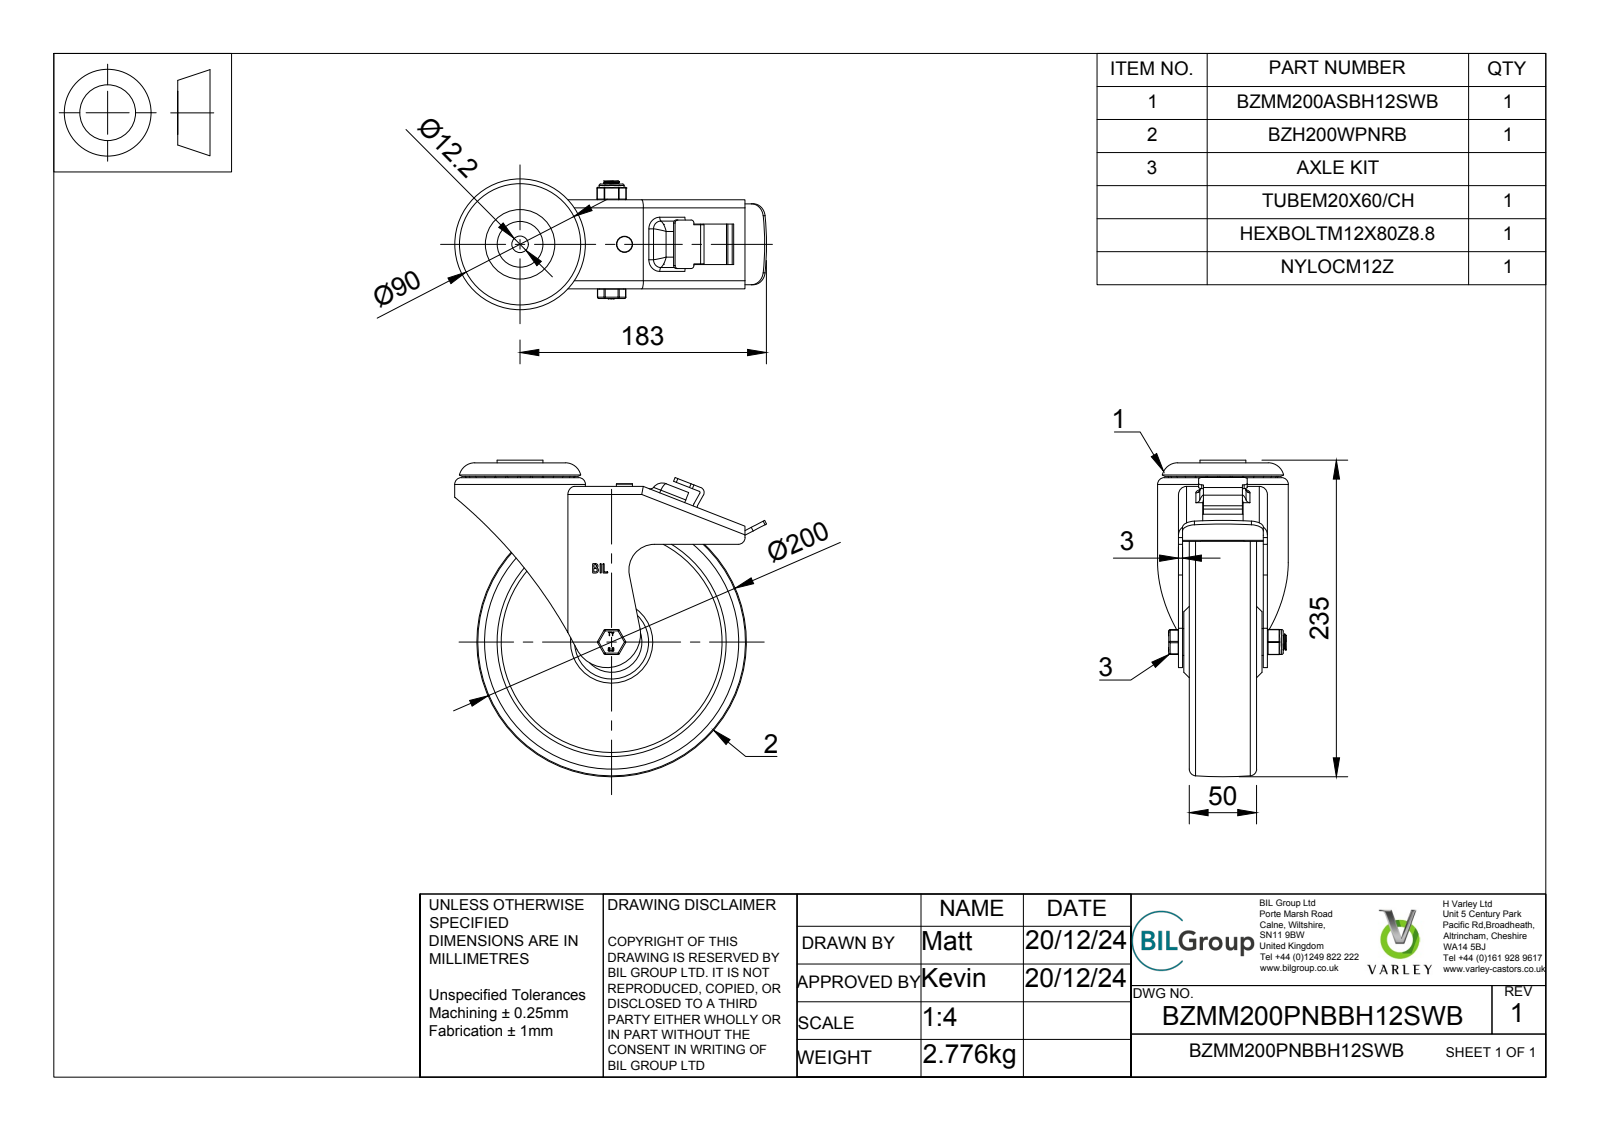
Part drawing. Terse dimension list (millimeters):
name: BZMM200PNBBH12SWB v3; BZMM200ASBH12SWB v1; ZINC PLATED, PRESSED STEEL HEAD; ZINC PLATED, PRESSED STEEL HEAD Geometry (+8 more)
written by: Autodesk Translation Framework v13.20.0.188 (AP242_MANAGED_MODEL_BASED_3D_ENGINEERING_MIM_LF)
unit: mm
bodies: 71 solids, 843 faces (397 planar, 280 cylindrical, 166 other)
size: 235 × 231.5 × 97
volume: 992 527 mm³; area: 351 566 mm²
holes: 1× ⌀6, 1× ⌀7, 1× ⌀10, 1× ⌀12, 1× ⌀12.2, 1× ⌀12.3, 1× ⌀12.5, 1× ⌀14, 1× ⌀20, 1× ⌀20.5, 1× ⌀30, 1× ⌀32
bosses: 10× ⌀5, 1× ⌀97, 1× ⌀78, 1× ⌀55, 1× ⌀39, 1× ⌀34, 1× ⌀29.5, 1× ⌀24
rounds: 30× R1.5, 24× R0.5, 13× R1, 12× R0.25, 10× R0.75, 10× R2, 6× R3, 6× R3.25
face distances: 3, 11, 4, 5, 35.5, 27.5, 38.5, 24.5, 63, 8
hole spacings: 77.5
